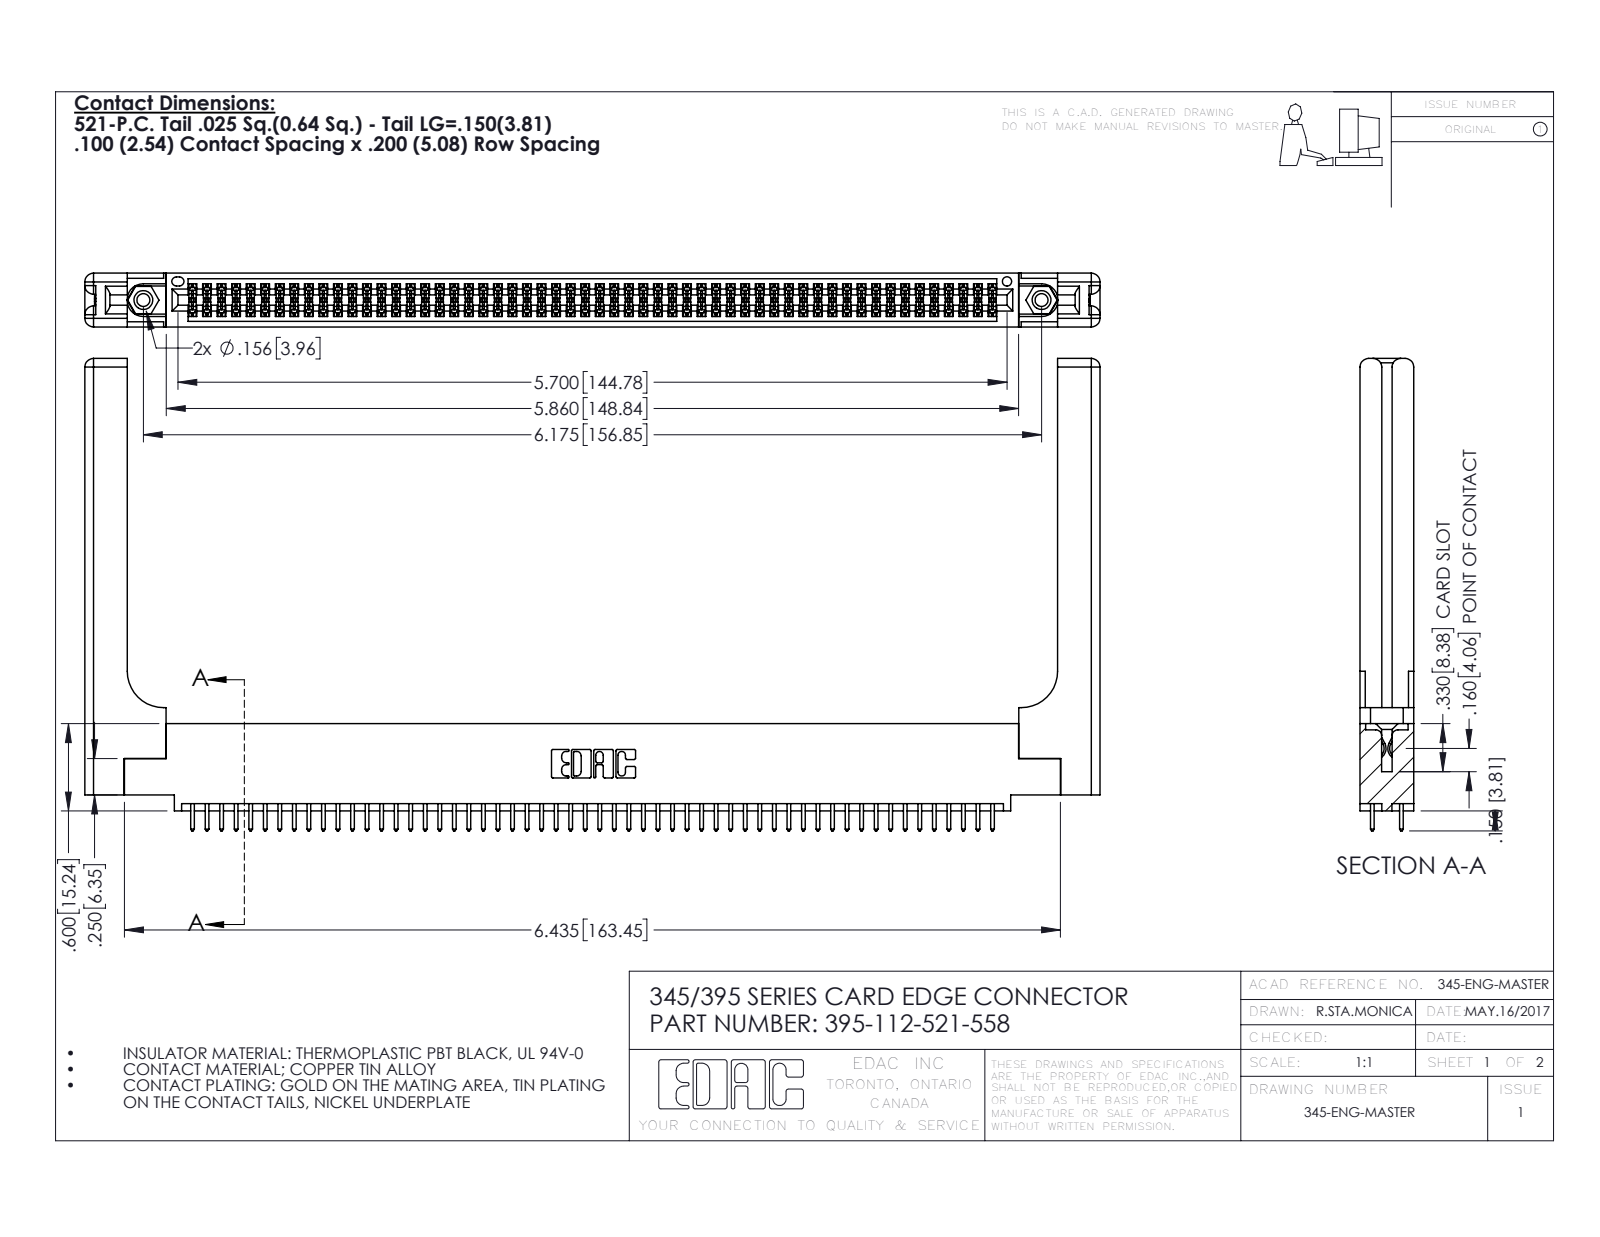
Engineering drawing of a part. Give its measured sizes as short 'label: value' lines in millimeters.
name: 345-220-058_345-220-058; 395-112-521-558; 345-292-001_345-293-121; 345-250-001_345-250-001-102 (+1 more)
written by: SolidWorks 2016 (CONFIG_CONTROL_DESIGN)
unit: mm
bodies: 117 solids, 5986 faces (3928 planar, 1998 cylindrical, 60 other)
size: 177.3 × 82.5 × 9.4
volume: 25 710 mm³; area: 30 590 mm²
holes: 2× ⌀2.3, 2× ⌀3.2, 2× ⌀4, 1× ⌀1.6
bosses: 2× ⌀3.9
rounds: 168× R0.2, 112× R0.3, 22× R0.3, 16× R1.5, 6× R0.2, 6× R0.8, 3× R0.7, 2× R0.4
face distances: 1.8, 7.6, 9.4, 2.5, 6.9, 0.6, 5.1, 5.7, 4.4, 3.8
hole spacings: 6.9, 150.9, 156.8
